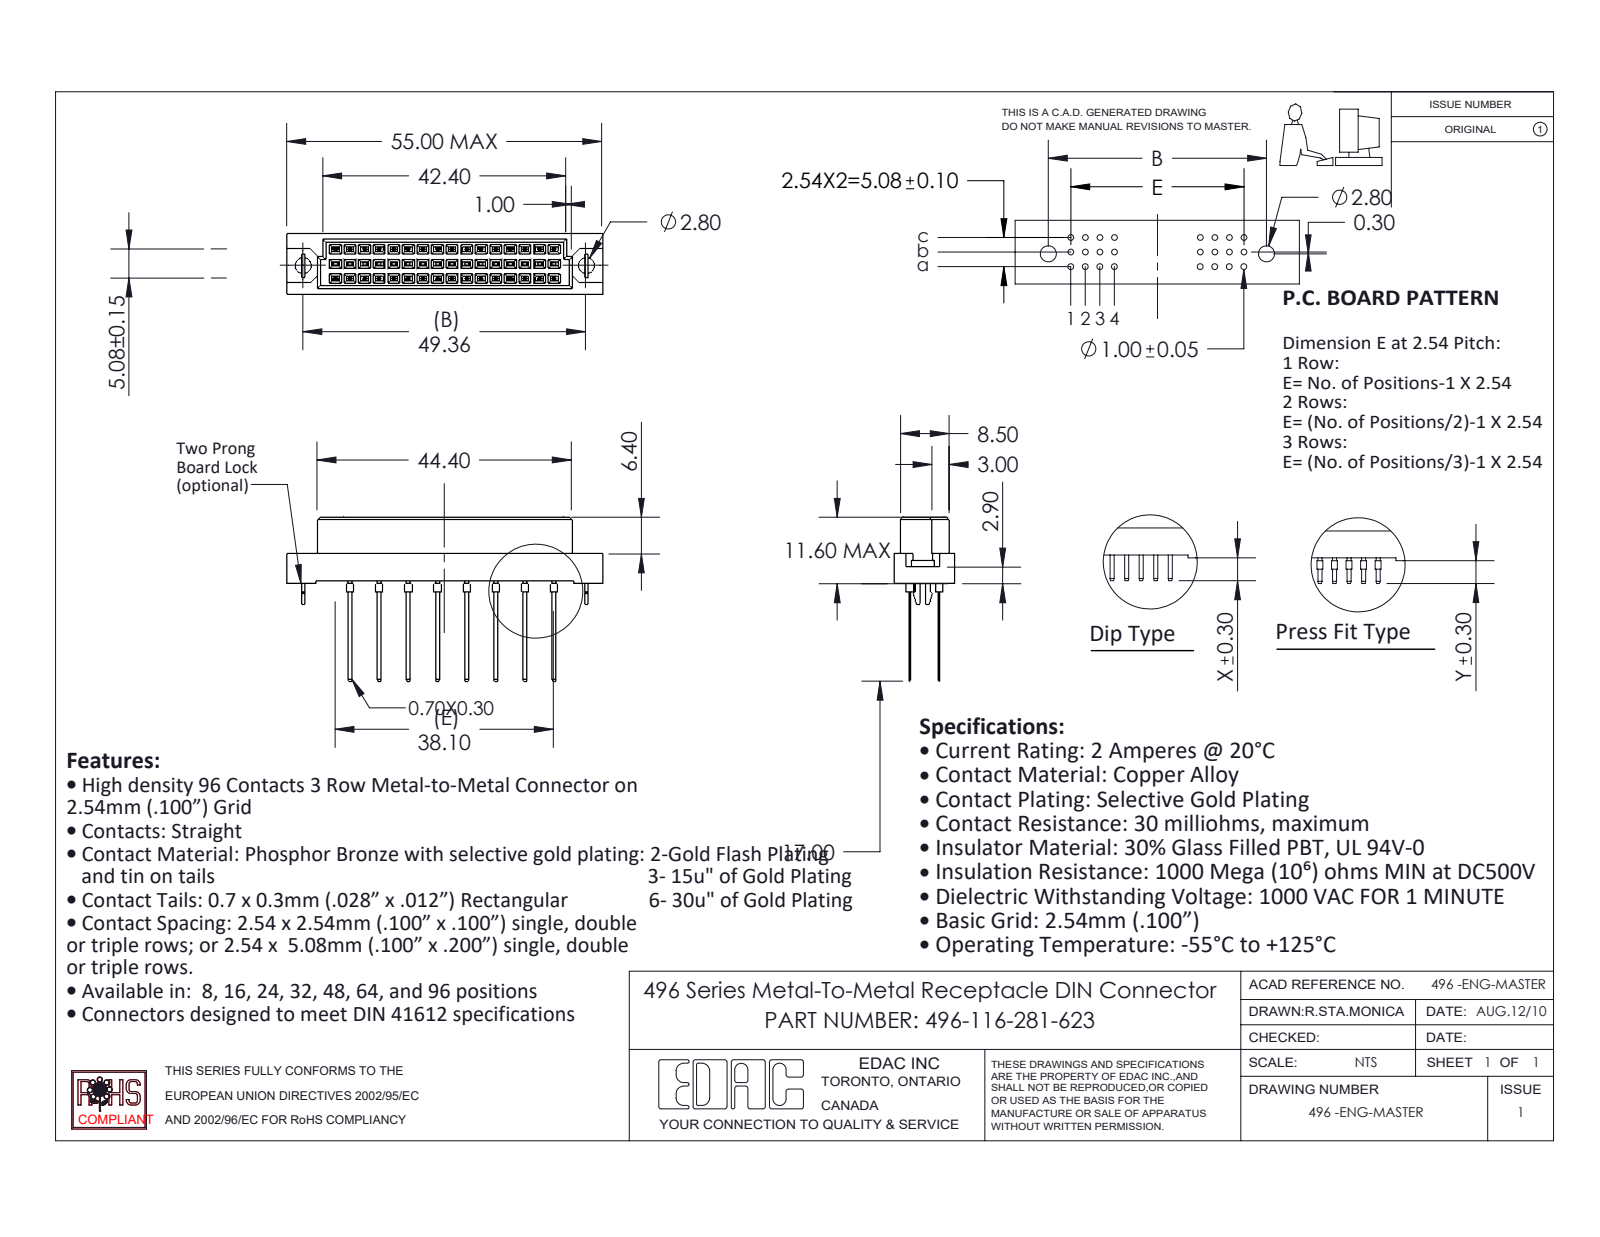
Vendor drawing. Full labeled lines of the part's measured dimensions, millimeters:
Part name (STEP PRODUCT): 496 Part_48; 496-116-281-623; 496-290_81; 496 Bore-lock
STEP written by: SolidWorks 2020 (CONFIG_CONTROL_DESIGN)
Units: millimetres
Bodies: 19 solids, 990 faces (952 planar, 38 cylindrical, 0 other)
Overall size (bounding box): 55 × 28.6 × 10.6
Volume: 4 698 mm³ · Surface area: 5 063 mm²
Round holes (diameter × count): ⌀2.8 ×2
Round bosses / shafts (diameter × count): ⌀1 ×16
Partial cylindrical surfaces — rounded edges, fillets, slot ends (radius × count): R0.53 ×1
Main face-to-face distances: 2.54, 5.08, 1.05, 9.55, 0.81, 1.56, 1.86, 0.56, 2.61, 2.91
Hole centre spacings: 49.36
